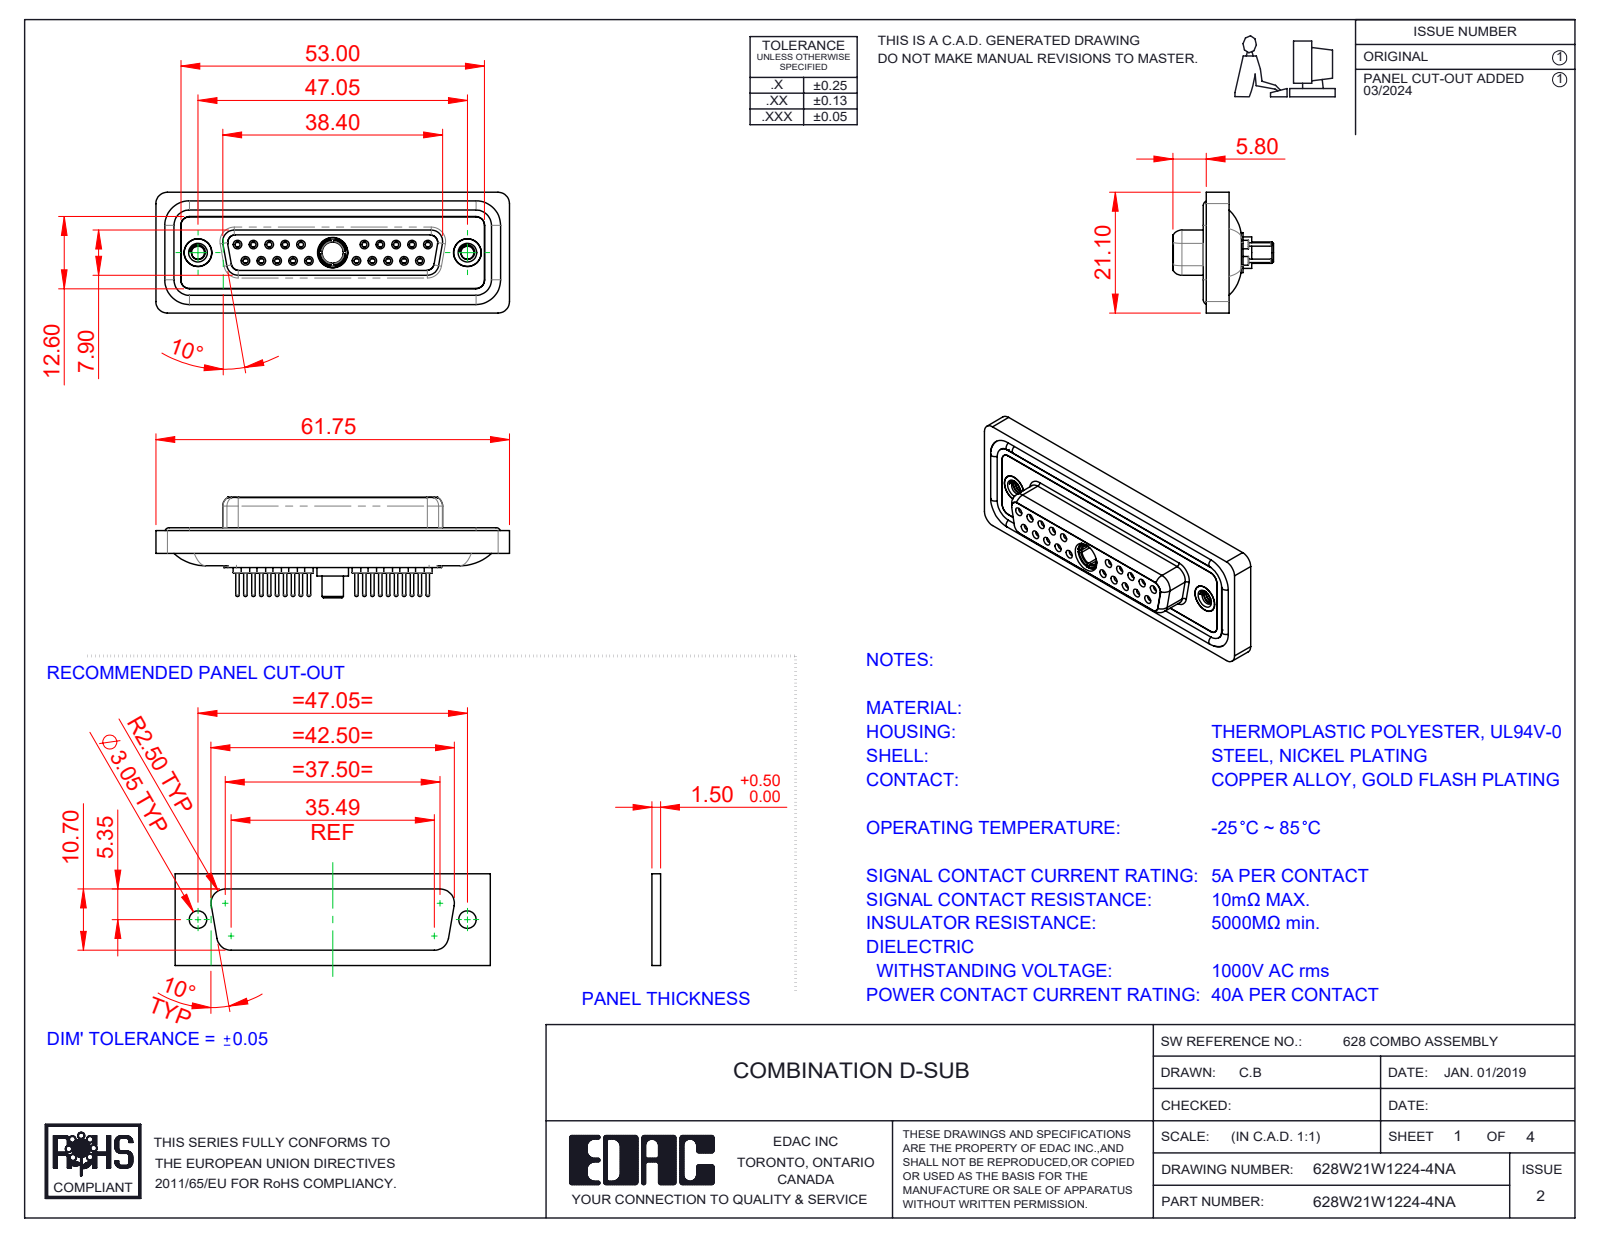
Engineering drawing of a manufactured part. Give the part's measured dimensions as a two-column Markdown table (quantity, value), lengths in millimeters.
| quantity | value |
| --- | --- |
| part name | Power Socket_40A S; 628Combo Waterproof Housing_25 Contacts; 628Combo Contact Row 2_24; 628Combo Shell Rear_25 Contacts (+5 more) |
| STEP written by | SolidWorks 2023 (CONFIG_CONTROL_DESIGN) |
| units | millimeters |
| bodies | 29 solids, 1558 faces (434 planar, 593 cylindrical, 531 other) |
| overall size | 61.75 × 21.1 × 17.55 |
| volume | 8 394 mm³ |
| surface area | 14 010 mm² |
| round holes (diameter × count) | 0.9 × 20, 1.1 × 20, 1.5 × 20, 2 × 20, 1.6 × 10, 1.7 × 10, 4.85 × 3, 2.26 × 2, 4 × 2, 4.05 × 2, 5 × 2, 3.7 × 1 |
| round bosses / shafts (diameter × count) | 2.2 × 20, 0.6 × 20, 1.6 × 14, 4.95 × 2, 4.8 × 2, 5.5 × 1, 5.2 × 1, 4.96 × 1 |
| partial cylindrical surfaces (radius × count) | 1.5 × 22, 2 × 18, 1.35 × 8, 1.6 × 8, 0.25 × 4, 0.5 × 4, 0.6 × 4, 0.65 × 4 |
| main face-to-face distances | 0.4, 1.8, 7.45, 6.6, 5.65, 0.5, 1.6, 7.05, 2.9, 1.1 |
| hole center spacings | 3.16, 2.77, 5.54, 5.03, 8.31, 7.48, 16.62, 19.39 |
